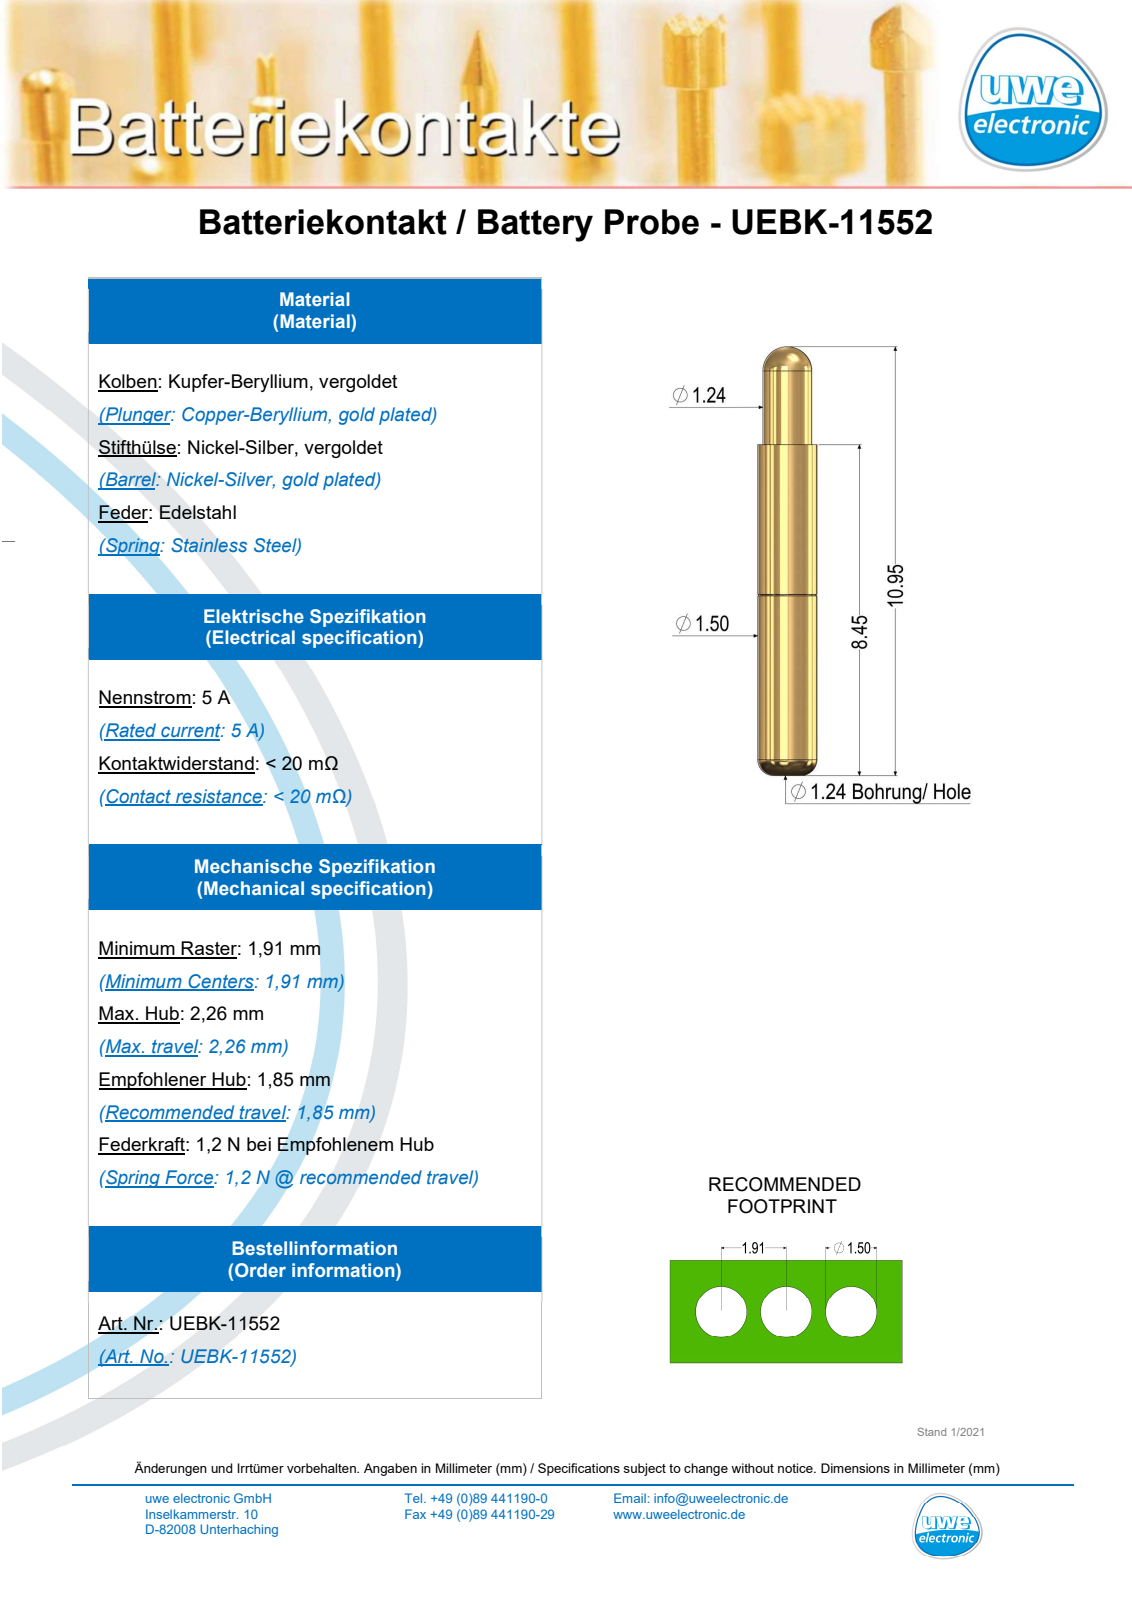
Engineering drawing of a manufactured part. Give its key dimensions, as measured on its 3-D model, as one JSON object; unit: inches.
{"part_name": "UEBK-11552", "step_written_by": "SolidWorks 2016 (AUTOMOTIVE_DESIGN)", "units": "inches", "bodies": {"solids": 1, "faces": 22, "planar": 2, "cylindrical": 8, "other": 12}, "overall_size": [0.428, 0.059, 0.059], "volume_in3": 0.001, "surface_area_in2": 0.079, "round_holes": [[0.025, 1]], "round_bosses_or_shafts": [[0.059, 1], [0.049, 1]], "face_to_face_distances": [0.322]}
